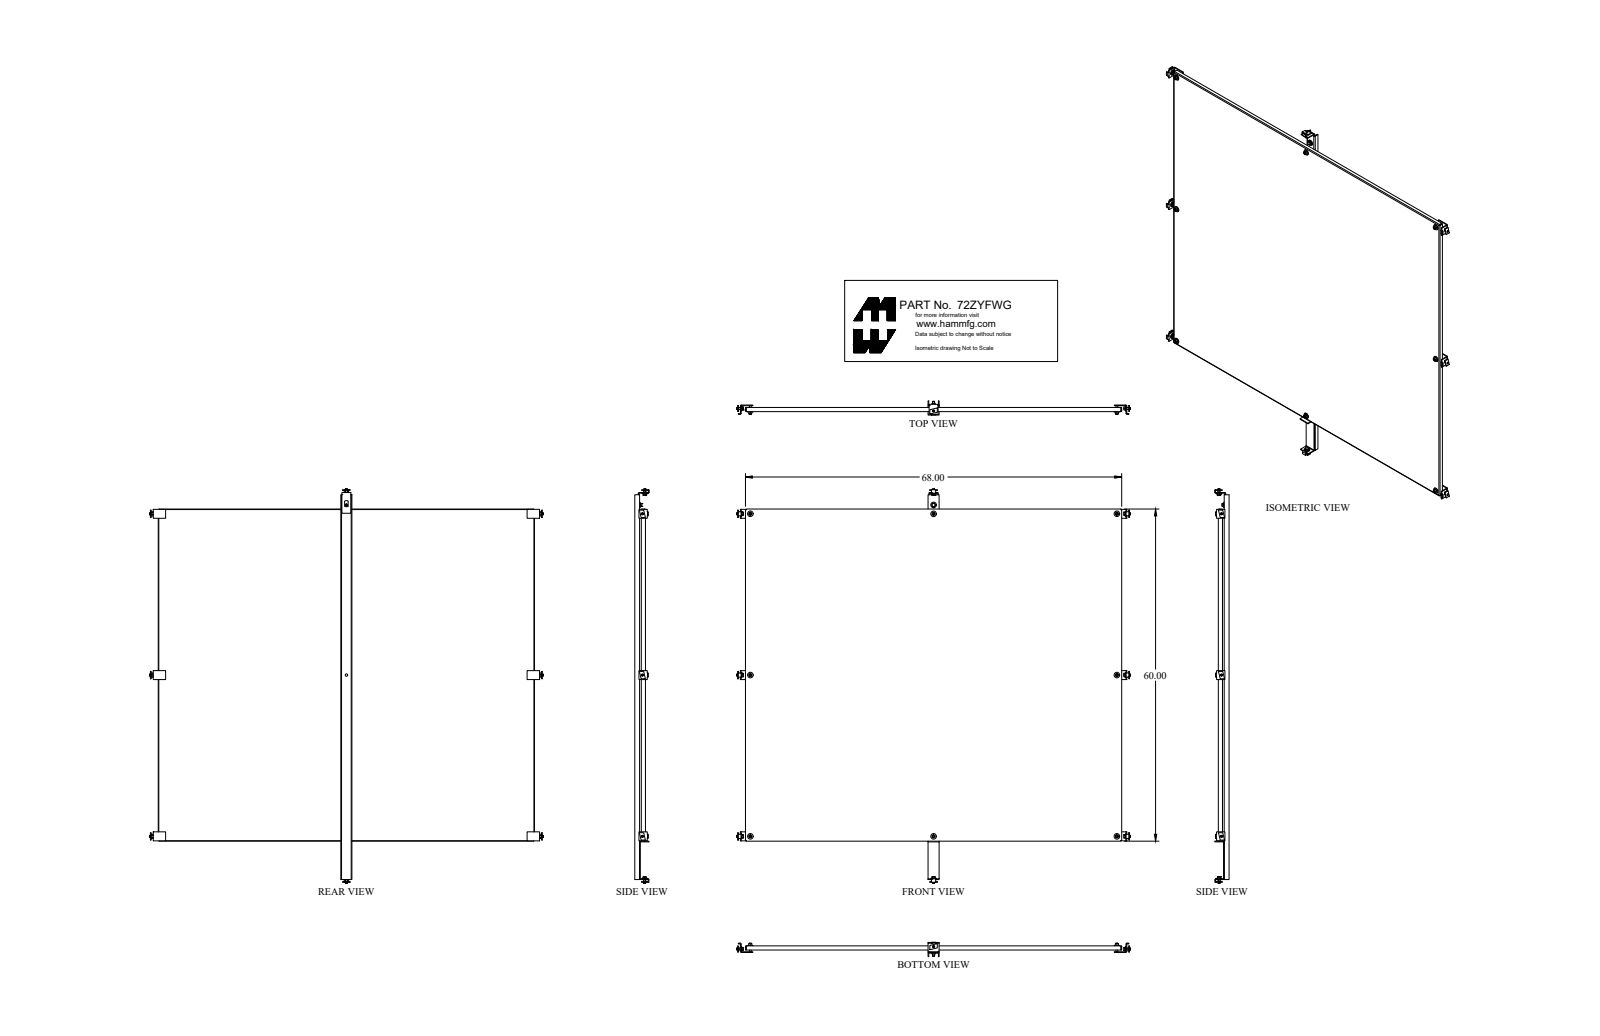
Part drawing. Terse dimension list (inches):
name: 72ZYFWG_Default
written by: SolidWorks 2018 (CONFIG_CONTROL_DESIGN)
unit: in
bodies: 18 solids, 385 faces (188 planar, 133 cylindrical, 64 other)
size: 70.906 × 70.582 × 2.593
volume: 441.2 in³; area: 9 149 in²
holes: 8× ⌀0.563, 6× ⌀0.437, 1× ⌀0.437, 1× ⌀0.453
bosses: 8× ⌀0.65, 8× ⌀0.33, 5× ⌀0.375, 3× ⌀0.375
rounds: 11× R0.06, 11× R0.185, 4× R0.048, 4× R0.143, 2× R0.219
face distances: 0.095, 0.125, 1.187, 1.062, 0.967, 1.092, 59.905, 33, 35, 67.905
hole spacings: 44.108, 67.01, 72.369, 29.125, 29.125, 33.125, 33.125, 58.25
